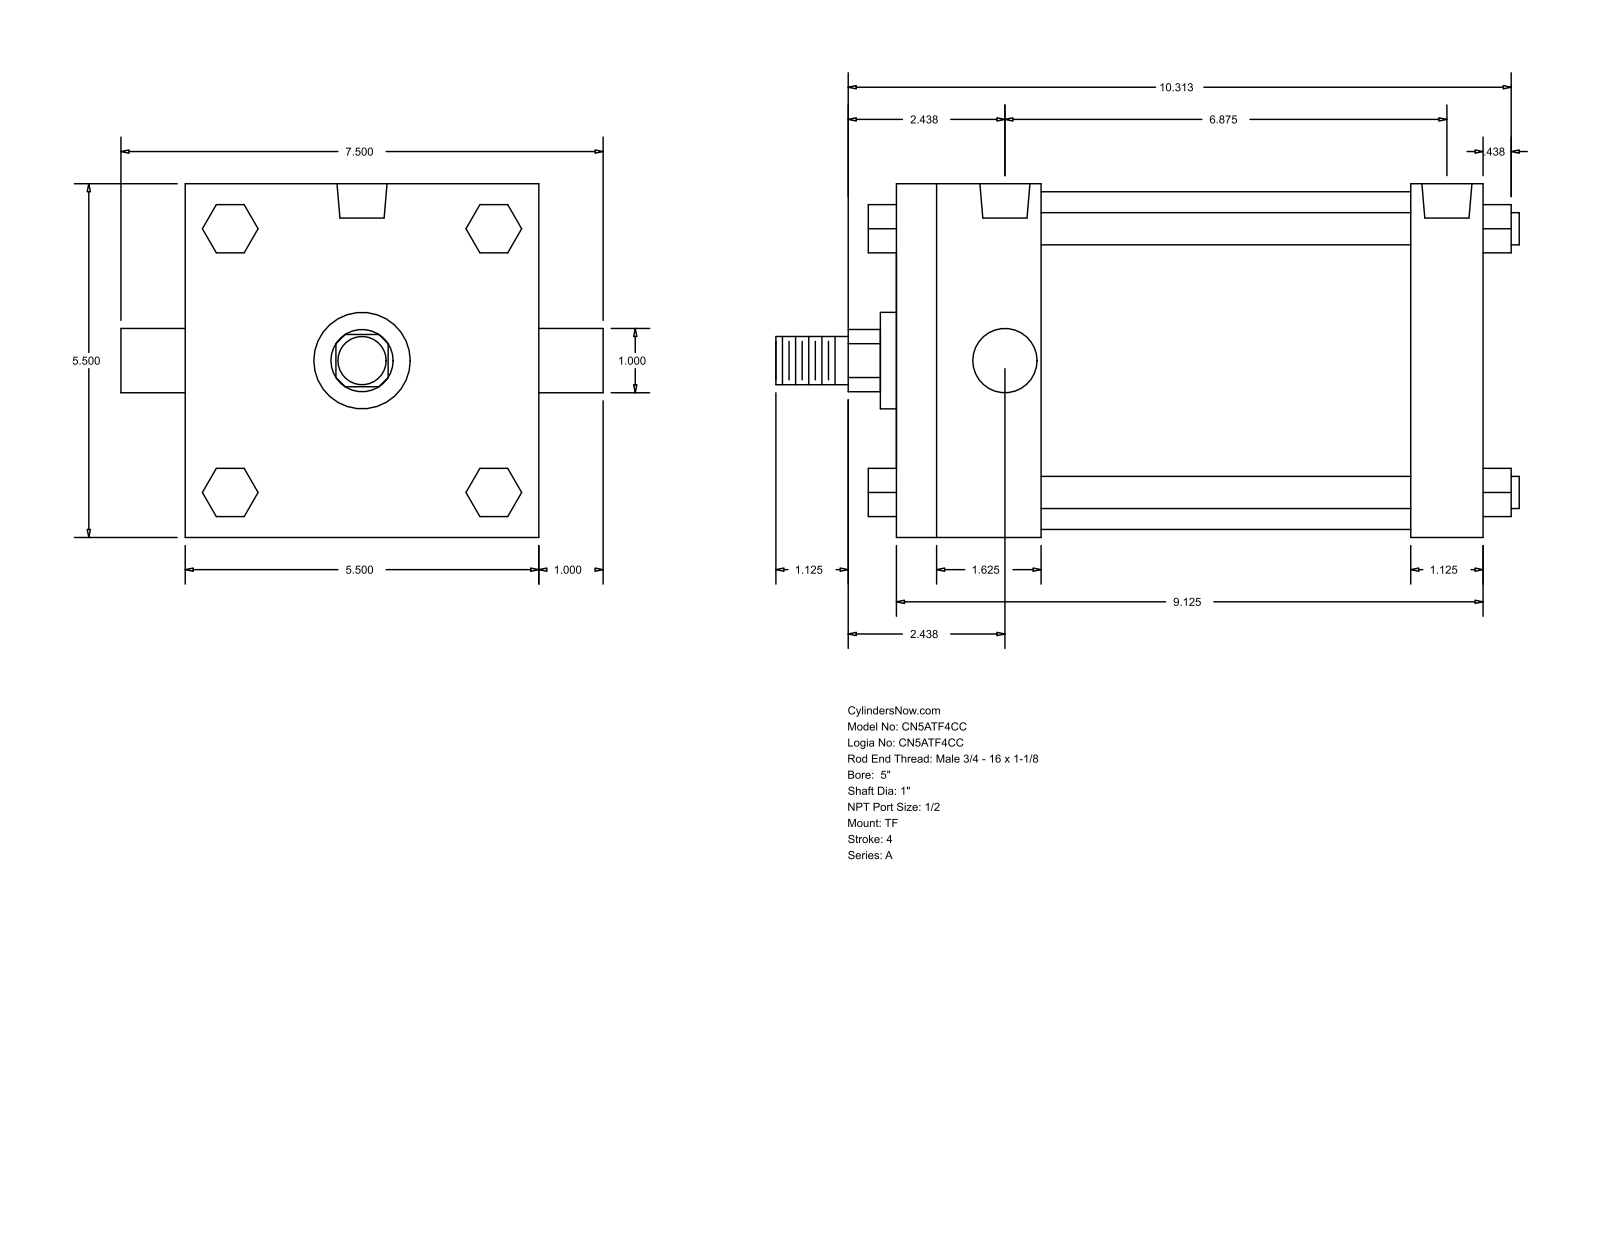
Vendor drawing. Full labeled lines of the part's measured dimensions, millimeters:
Part name (STEP PRODUCT): A_TF__0500_1
STEP written by: GSSL Pune (CONFIG_CONTROL_DESIGN)
Units: millimetres
Bodies: 0 solids, 120 faces (92 planar, 28 cylindrical, 0 other)
Overall size (bounding box): 293.69 × 190.5 × 139.7
Round holes (diameter × count): ⌀8.73 ×3, ⌀19.77 ×2
Round bosses / shafts (diameter × count): ⌀12.7 ×4, ⌀25.4 ×2, ⌀133.35 ×1, ⌀38.1 ×1, ⌀19.05 ×1
Partial cylindrical surfaces — rounded edges, fillets, slot ends (radius × count): R12.29 ×1
Main face-to-face distances: 139.7, 231.77, 28.57, 203.2, 57.15, 146.05, 174.62, 19.05, 52.07, 90.18
Hole centre spacings: 2.39, 172.24, 169.85, 174.63
